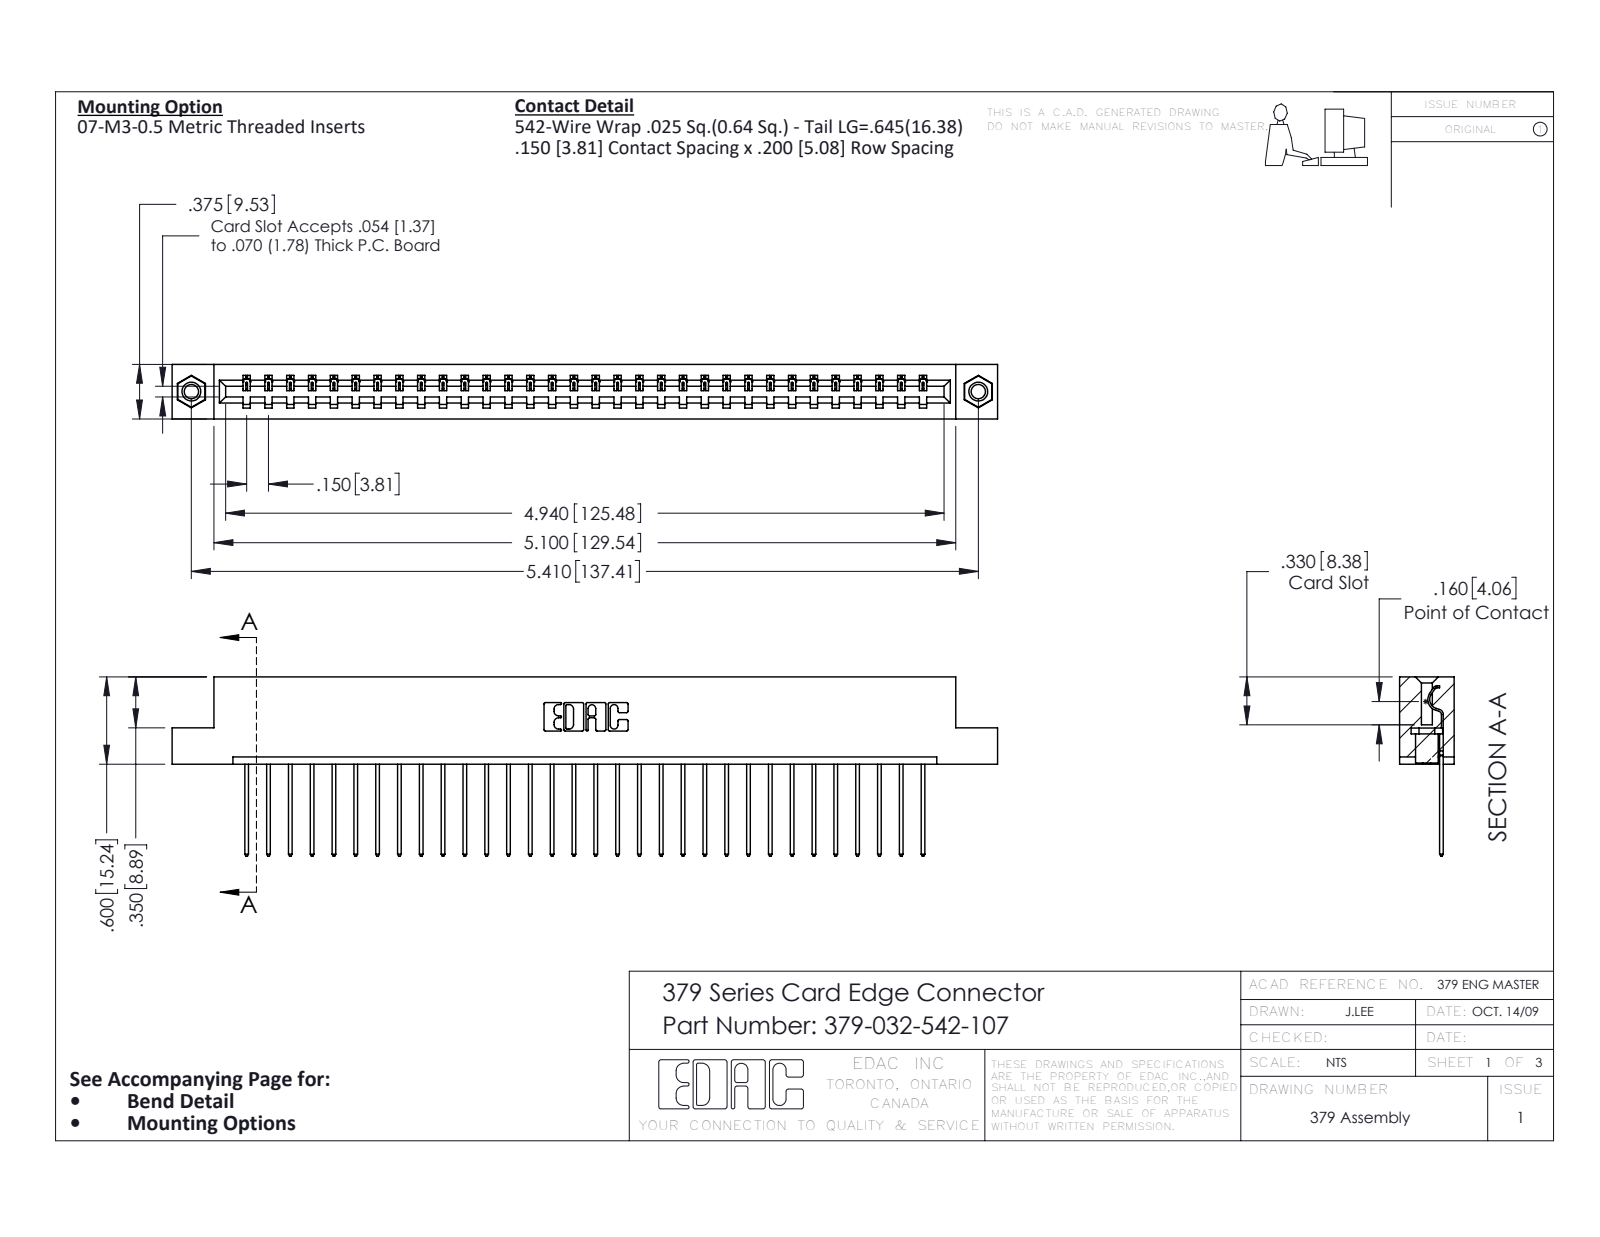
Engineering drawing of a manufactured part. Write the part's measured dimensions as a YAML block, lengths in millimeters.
part_name: "379 Part_Flush - .156 Dia - TI; 379-032-542-107; 345-292-001_345-293-142; 345-250-001_345-250-005-103"
step_written_by: "SolidWorks 2016 (CONFIG_CONTROL_DESIGN)"
units: millimeters
bodies: {solids: 35, faces: 2030, planar: 1446, cylindrical: 568, other: 16}
overall_size: [144.1, 31.3, 9.5]
volume: 15100
surface_area: 15890
round_holes:
  - {diameter: 2.5, count: 2}
  - {diameter: 3.2, count: 2}
  - {diameter: 4, count: 2}
round_bosses_or_shafts:
  - {diameter: 3.9, count: 2}
partial_cylinders:
  - {radius: 0.2, count: 64}
  - {radius: 0.3, count: 64}
  - {radius: 0.3, count: 22}
  - {radius: 0.2, count: 6}
  - {radius: 0.8, count: 6}
  - {radius: 0.7, count: 3}
  - {radius: 0.4, count: 1}
  - {radius: 0.6, count: 1}
face_to_face_distances: [7.6, 1.9, 9.5, 5.7, 7, 2.5, 0.6, 5.1, 15.2, 14]
hole_center_spacings: [137.4]
